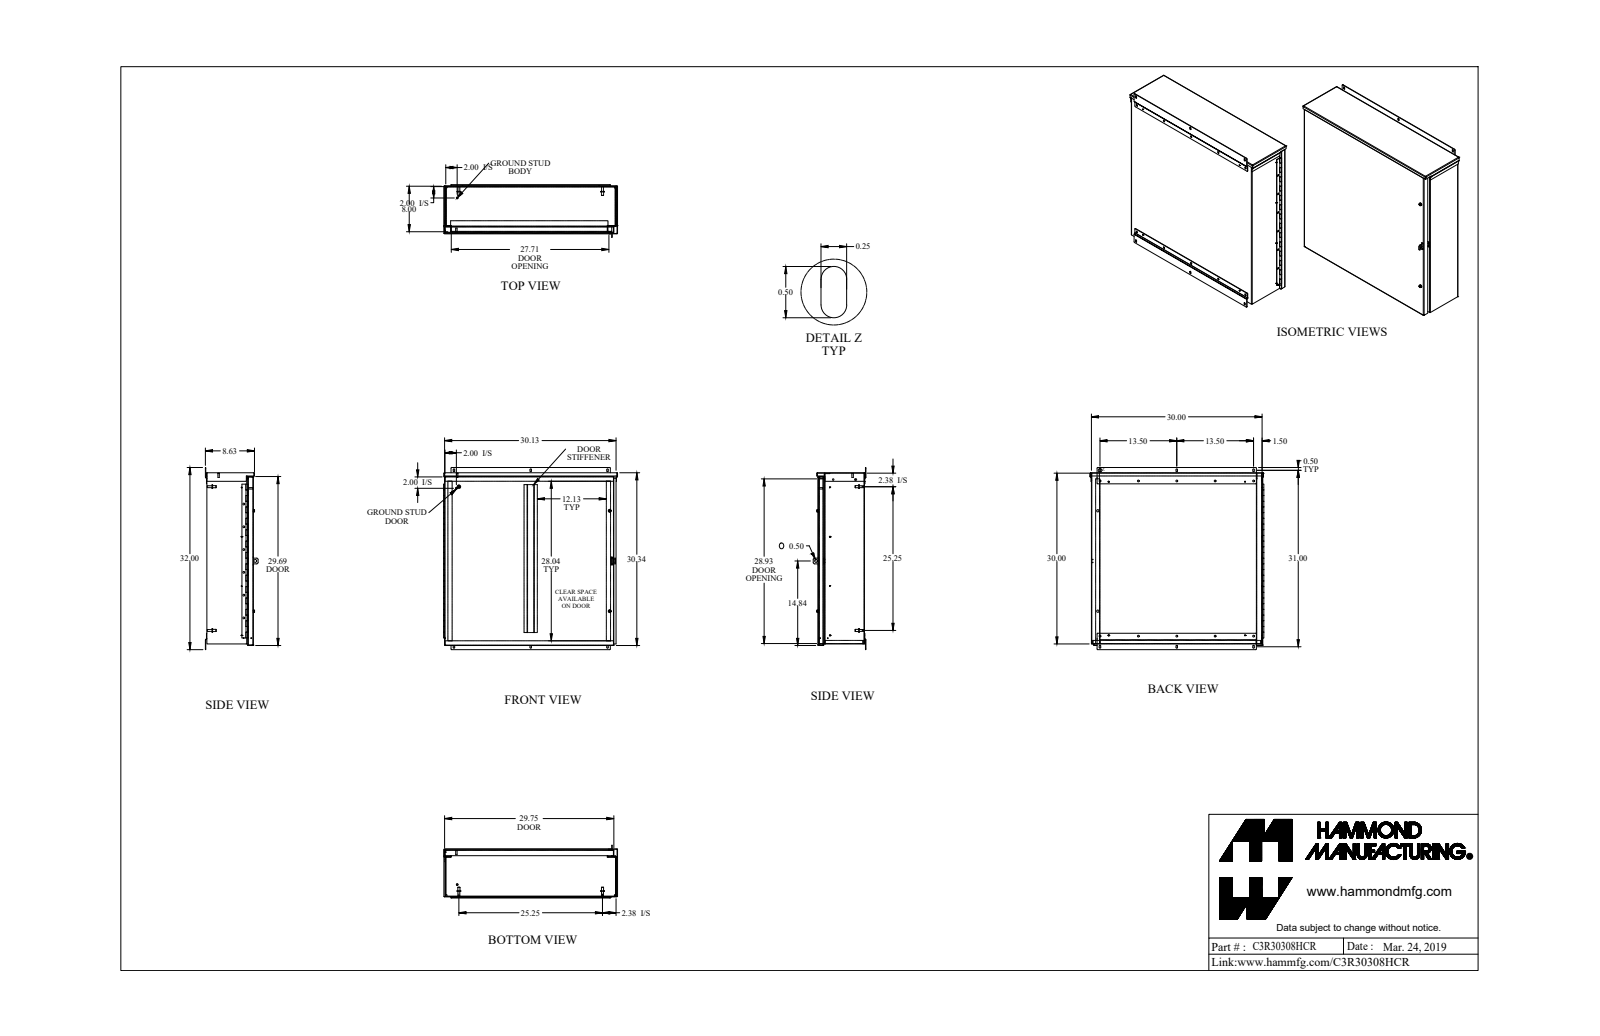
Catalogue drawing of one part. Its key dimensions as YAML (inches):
part_name: "C3R30308HCR_Default"
step_written_by: "SolidWorks 2019 (CONFIG_CONTROL_DESIGN)"
units: inches
bodies: {solids: 35, faces: 1010, planar: 549, cylindrical: 407, other: 54}
overall_size: [32, 30.571, 9.26]
volume: 269.3
surface_area: 7320
round_holes:
  - {diameter: 0.312, count: 10}
  - {diameter: 0.304, count: 6}
  - {diameter: 0.137, count: 4}
  - {diameter: 0.14, count: 4}
  - {diameter: 0.25, count: 3}
  - {diameter: 0.26, count: 3}
  - {diameter: 0.313, count: 3}
  - {diameter: 0.266, count: 2}
  - {diameter: 0.28, count: 2}
  - {diameter: 0.29, count: 2}
  - {diameter: 0.397, count: 2}
  - {diameter: 0.188, count: 1}
round_bosses_or_shafts:
  - {diameter: 0.131, count: 10}
  - {diameter: 0.65, count: 4}
  - {diameter: 0.375, count: 4}
  - {diameter: 0.33, count: 4}
  - {diameter: 0.51, count: 3}
  - {diameter: 0.244, count: 3}
  - {diameter: 0.187, count: 3}
  - {diameter: 0.5, count: 2}
partial_cylinders:
  - {radius: 0.036, count: 39}
  - {radius: 0.108, count: 39}
  - {radius: 0.125, count: 23}
  - {radius: 0.171, count: 3}
  - {radius: 0.25, count: 2}
face_to_face_distances: [0.072, 8.1, 8.172, 8.028, 30, 29.928, 0.259, 0.187, 30.072, 29.856]
hole_center_spacings: [6.75, 28.074, 4, 13.5, 30.411, 27.25, 1.505, 5.252]
